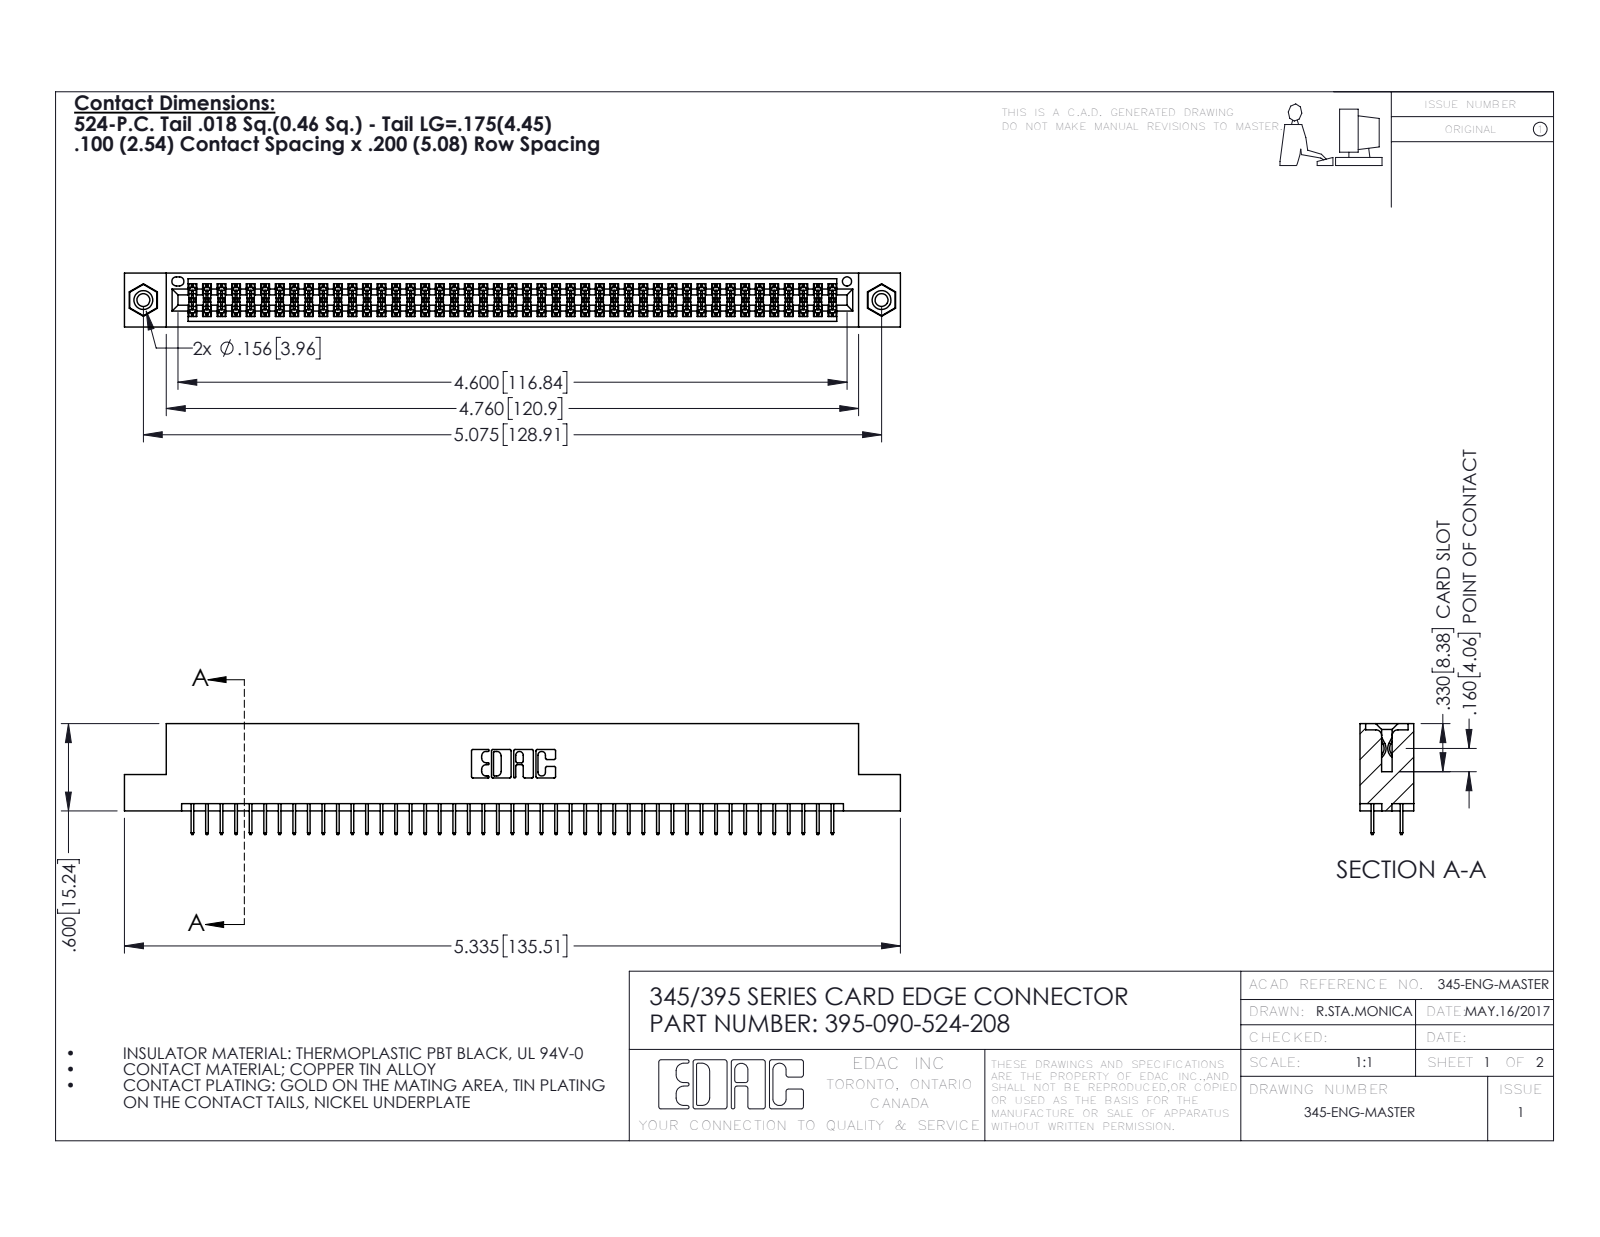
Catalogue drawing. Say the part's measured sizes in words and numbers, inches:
The part is named "345-292-001_345-293-124; 345-250-001_345-250-003-102; 395-090-524-208; 345 Part_Flush Mounting Lugs - 0.156 Dia-TI". Its 3-D file was written by "SolidWorks 2016 (CONFIG_CONTROL_DESIGN)". It is 93 solids with 5046 faces: 3622 planar, 1408 cylindrical and 16 other. Overall it measures 5.335 by 0.762 by 0.37 inches. Its volume is 0.796 cubic inches and its surface area 29.45 square inches. Round holes: 2 of diameter 0.089, 2 of diameter 0.125, 2 of diameter 0.156, 1 of diameter 0.064. Round bosses or shafts: 2 of diameter 0.155. Partial cylindrical surfaces (rounded edges, fillets, slot ends): 135 of radius 0.006, 22 of radius 0.01, 6 of radius 0.007, 6 of radius 0.031, 3 of radius 0.026, 2 of radius 0.014, 2 of radius 0.019, 2 of radius 0.022. The main face-to-face distances are 0.072, 0.298, 0.2, 0.37, 0.098, 0.272, 0.025, 0.225, 0.072, 0.175. The hole center spacings are 0.27, 4.839, 5.075.
